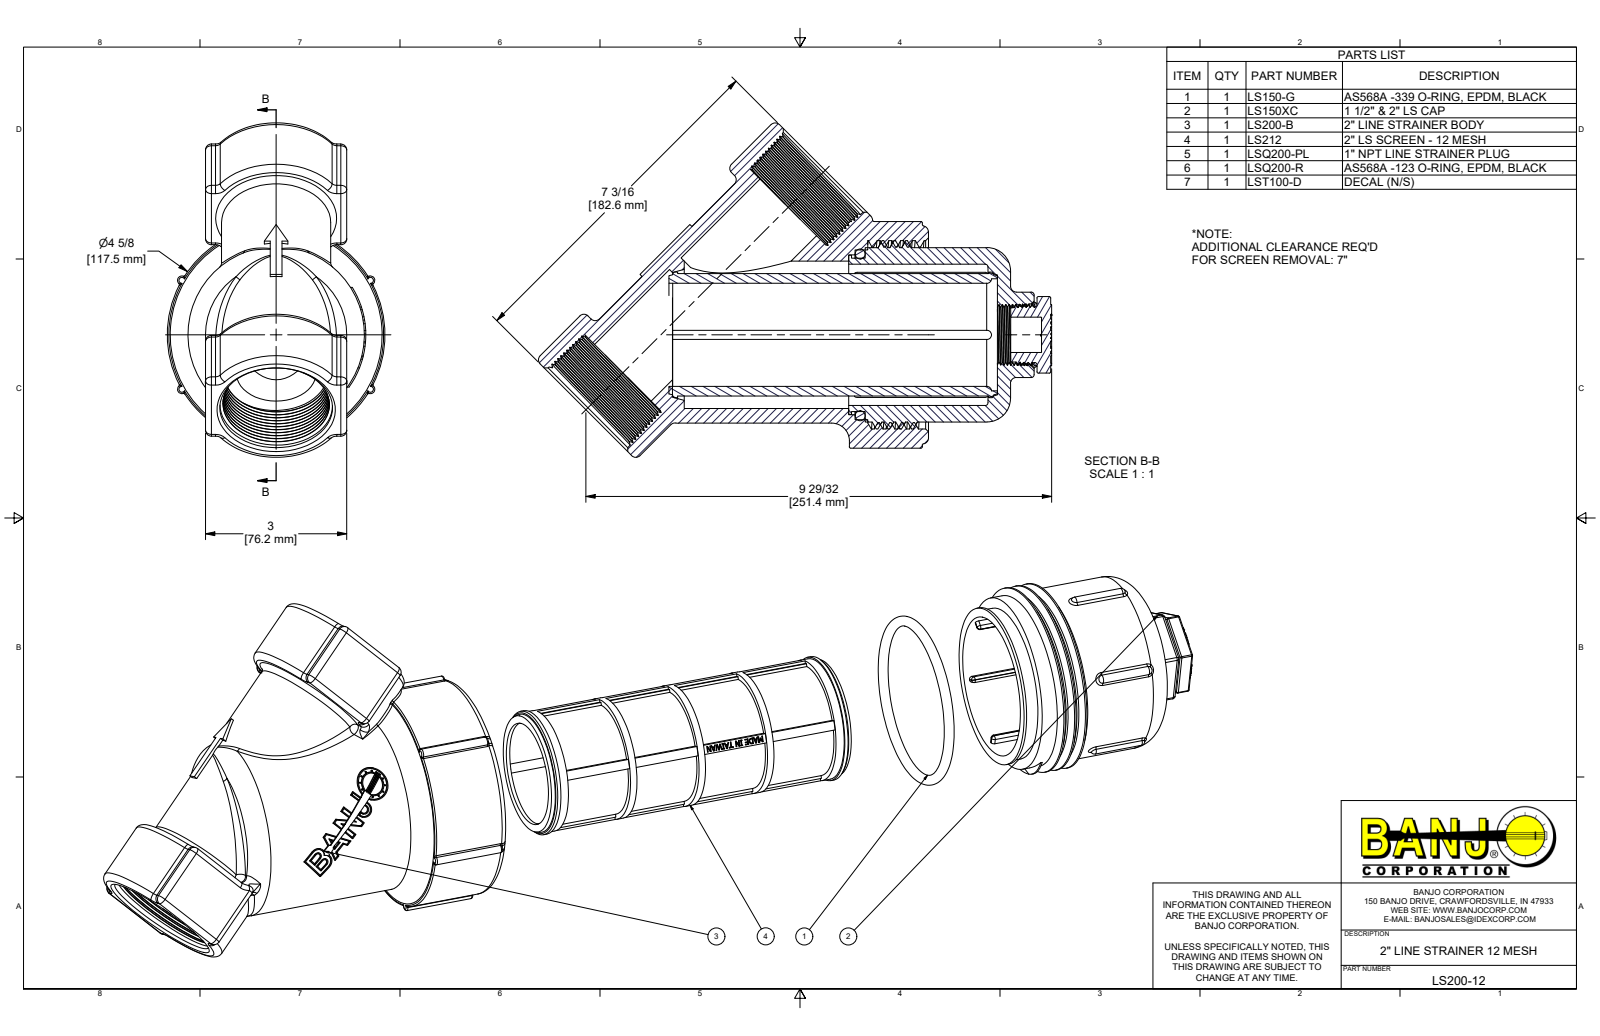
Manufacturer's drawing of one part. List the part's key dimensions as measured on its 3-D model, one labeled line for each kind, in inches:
Part name (STEP PRODUCT): LS200-B; LS150XC; LSQ200-PL; LSQ200-R (+4 more)
STEP written by: Autodesk Inventor 2014 (AUTOMOTIVE_DESIGN)
Units: inches
Bodies: 5 solids, 1454 faces (659 planar, 270 cylindrical, 525 other)
Overall size (bounding box): 10.905 × 7.102 × 4.625
Volume: 54.95 in³ · Surface area: 488.2 in²
Round holes (diameter × count): ⌀1.7 ×2, ⌀0.454 ×1, ⌀0.641 ×1, ⌀0.75 ×1, ⌀1.176 ×1, ⌀2.19 ×1, ⌀2.35 ×1, ⌀3 ×1, ⌀3.13 ×1, ⌀3.395 ×1, ⌀3.605 ×1, ⌀3.729 ×1
Round bosses / shafts (diameter × count): ⌀4.625 ×1, ⌀3.75 ×1, ⌀3.702 ×1, ⌀3.38 ×1, ⌀3.257 ×1, ⌀2.666 ×1, ⌀2.6 ×1, ⌀2.38 ×1
Partial cylindrical surfaces — rounded edges, fillets, slot ends (radius × count): R0.06 ×46, R0.125 ×35, R0.03 ×30, R0.094 ×12, R0.1 ×4, R0.12 ×3, R0.065 ×2, R0.082 ×2
Main face-to-face distances: 3, 3.16, 1.745, 2.785, 1.595, 1.445, 1.34, 0.2, 0.35, 2.81
